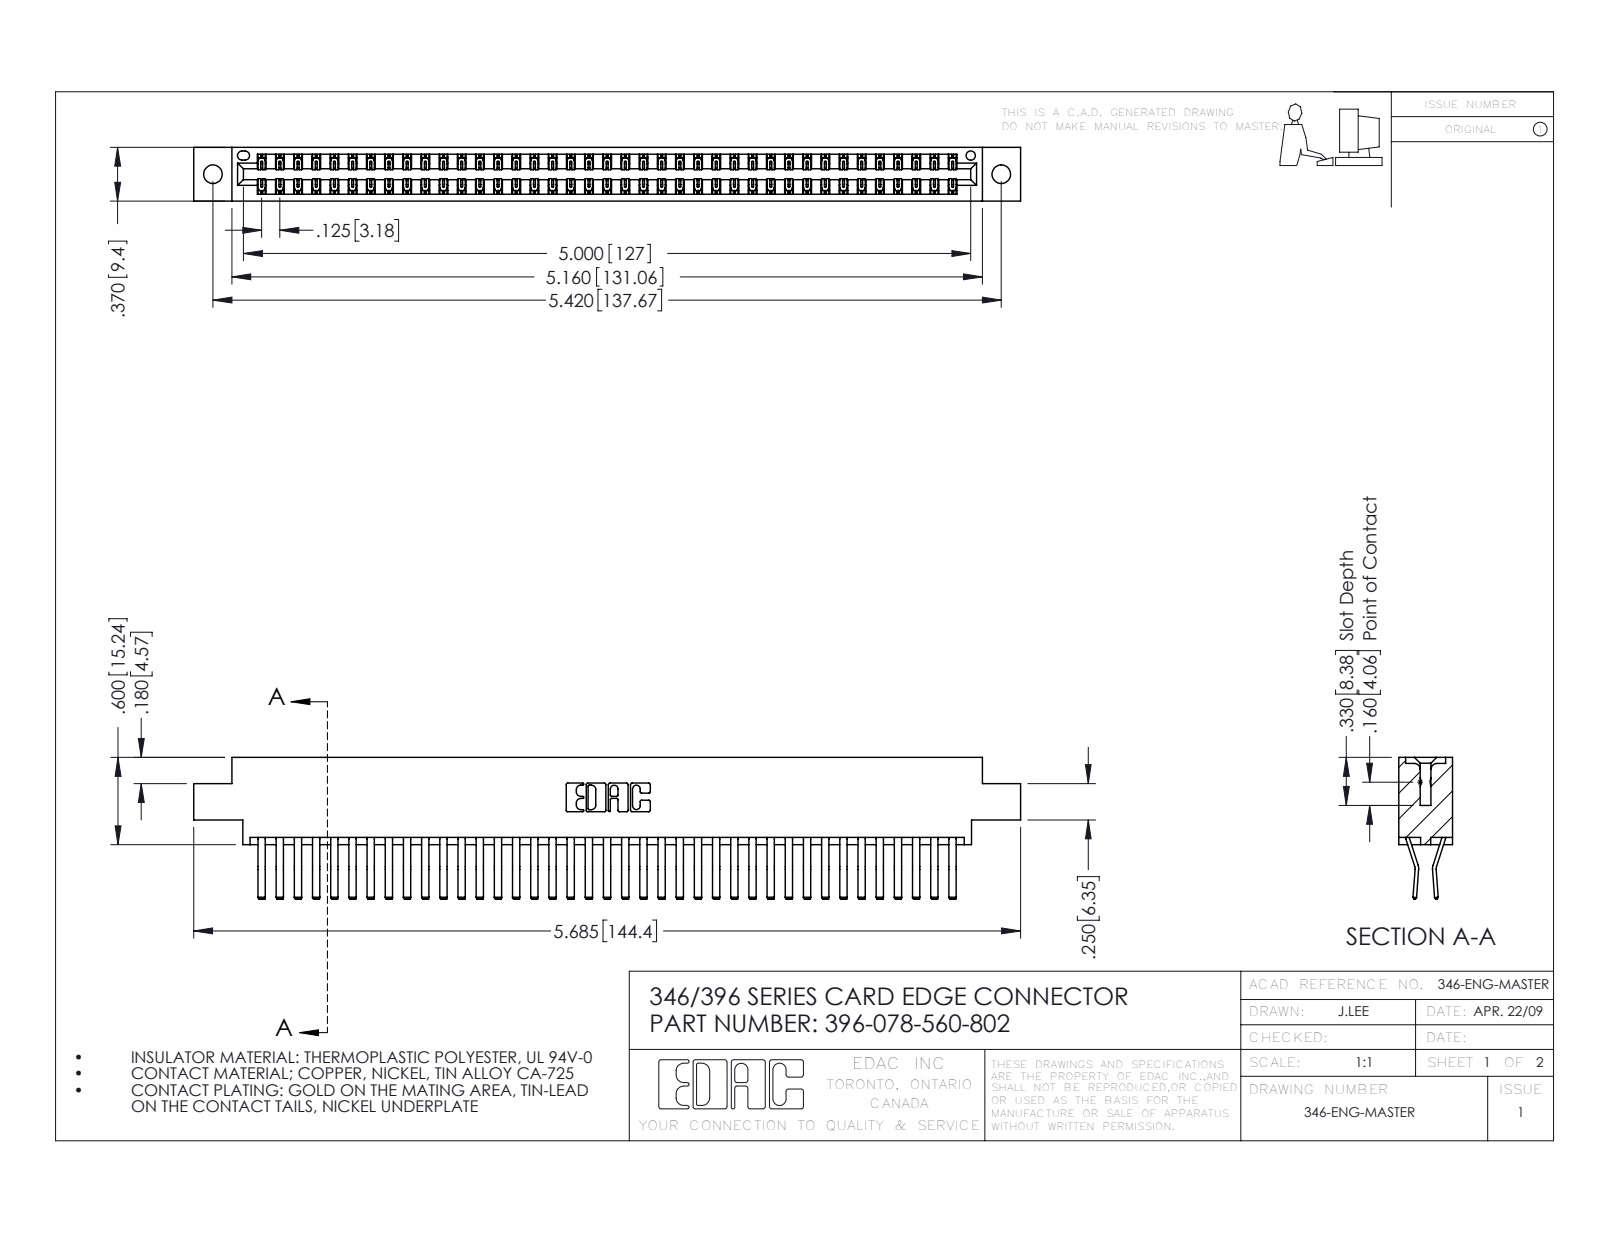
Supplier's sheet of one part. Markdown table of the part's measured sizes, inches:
| quantity | value |
| --- | --- |
| part name | 345-292-001_560 Tail; 346 Part_0.170 Offset - 0.128 Dia; 396-078-560-802 |
| STEP written by | SolidWorks 2016 (CONFIG_CONTROL_DESIGN) |
| units | inches |
| bodies | 79 solids, 4338 faces (2810 planar, 1528 cylindrical, 0 other) |
| overall size | 5.685 × 0.975 × 0.37 |
| volume | 0.877 in³ |
| surface area | 32.53 in² |
| round holes (diameter × count) | 0.128 × 2, 0.064 × 1 |
| partial cylindrical surfaces (radius × count) | 0.006 × 117, 0.01 × 22, 0.007 × 6, 0.031 × 6, 0.026 × 3, 0.01 × 2, 0.014 × 2, 0.022 × 2 |
| main face-to-face distances | 0.048, 0.322, 0.37, 0.025, 0.25, 0.072, 0.298, 0.275, 0.148, 0.222 |
| hole center spacings | 0.246, 5.211, 5.42 |
